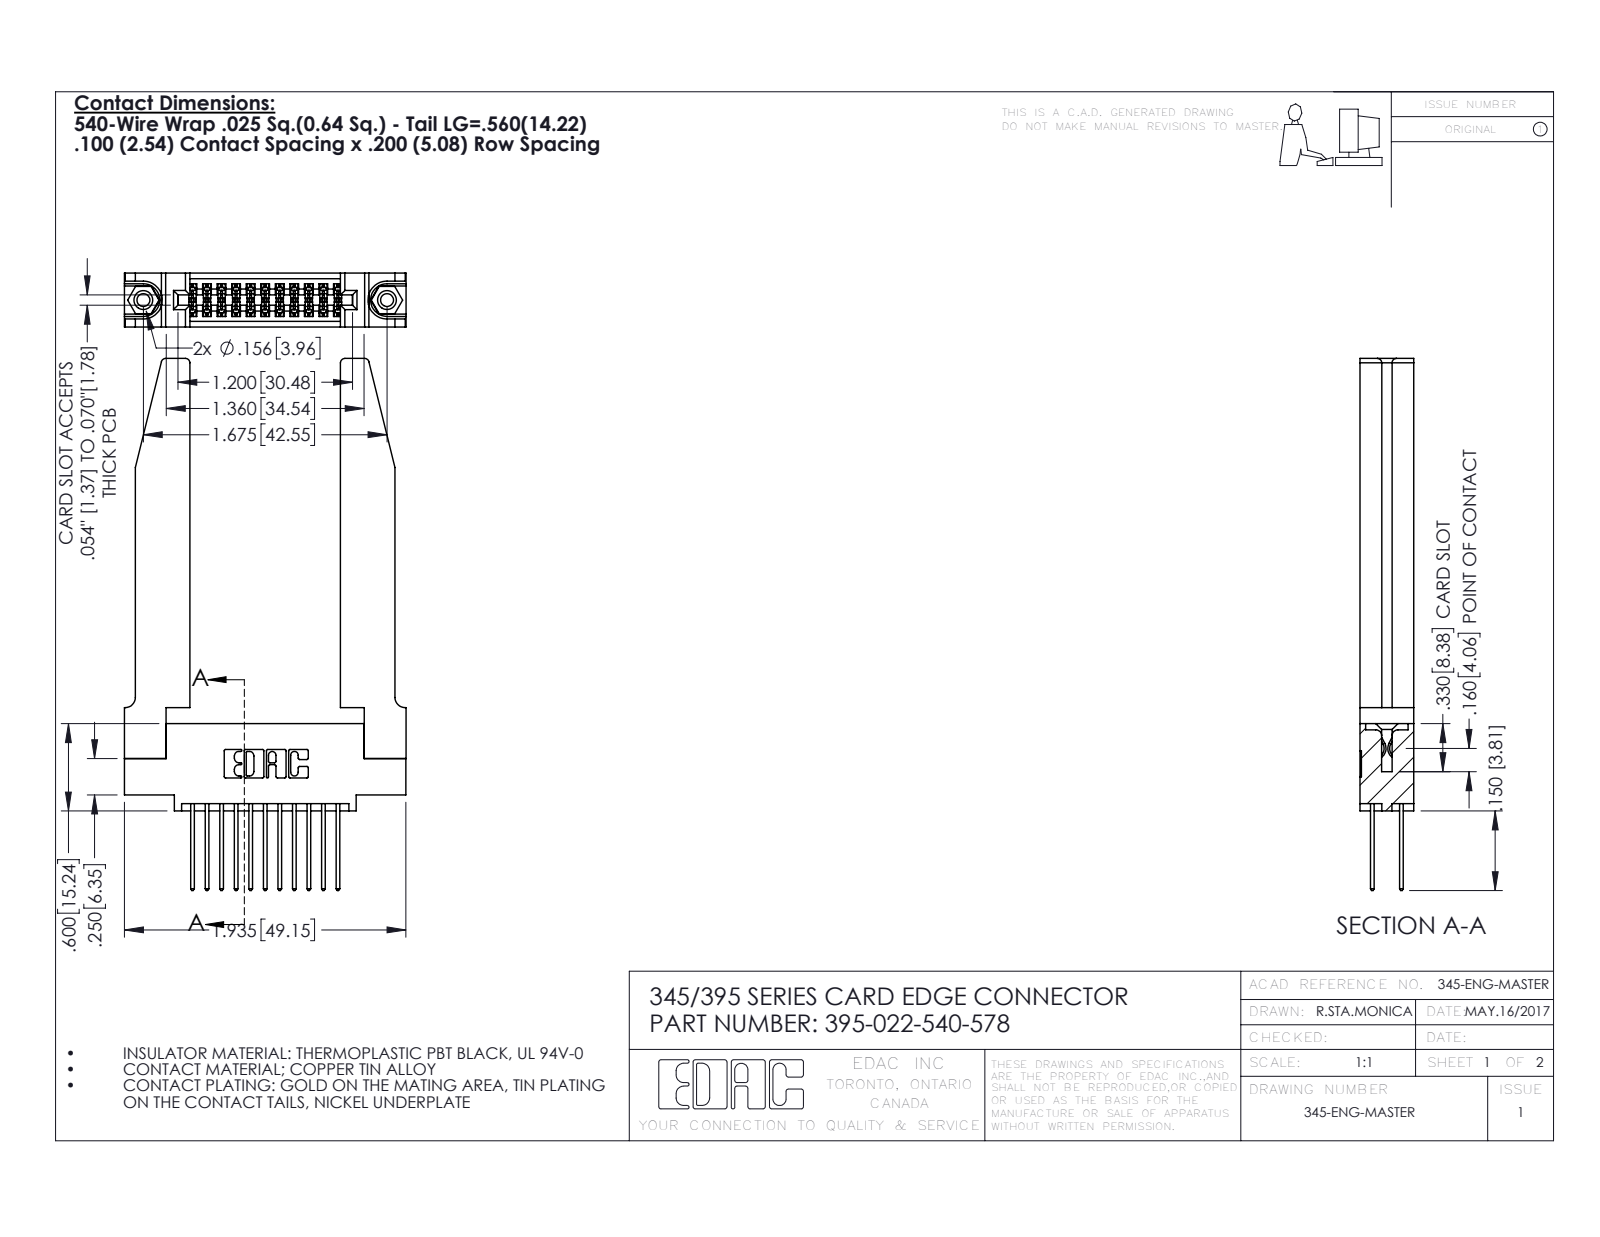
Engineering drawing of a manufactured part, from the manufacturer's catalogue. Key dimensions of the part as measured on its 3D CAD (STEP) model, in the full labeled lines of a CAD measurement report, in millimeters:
Part name (STEP PRODUCT): 345-220-078_345-220-078; 345 Part_0.110 Offset - 0.156 Dia-TH; 395-022-540-578; 345-292-001_345-293-140 (+1 more)
STEP written by: SolidWorks 2016 (CONFIG_CONTROL_DESIGN)
Units: millimetres
Bodies: 27 solids, 1464 faces (952 planar, 460 cylindrical, 52 other)
Overall size (bounding box): 92.9 × 49.2 × 9.4
Volume: 12 300 mm³ · Surface area: 13 370 mm²
Round holes (diameter × count): ⌀2.3 ×2, ⌀3.2 ×2, ⌀4 ×2, ⌀1.6 ×1
Round bosses / shafts (diameter × count): ⌀3.9 ×2
Partial cylindrical surfaces — rounded edges, fillets, slot ends (radius × count): R0.2 ×33, R0.3 ×22, R0.3 ×22, R0.8 ×8, R0.2 ×6, R0.8 ×6, R0.7 ×3, R0.4 ×2
Main face-to-face distances: 9.4, 1.8, 7.6, 5.1, 3.8, 3.8, 2.5, 6.9, 0.6, 5.6
Hole centre spacings: 6.9, 36.7, 42.5
